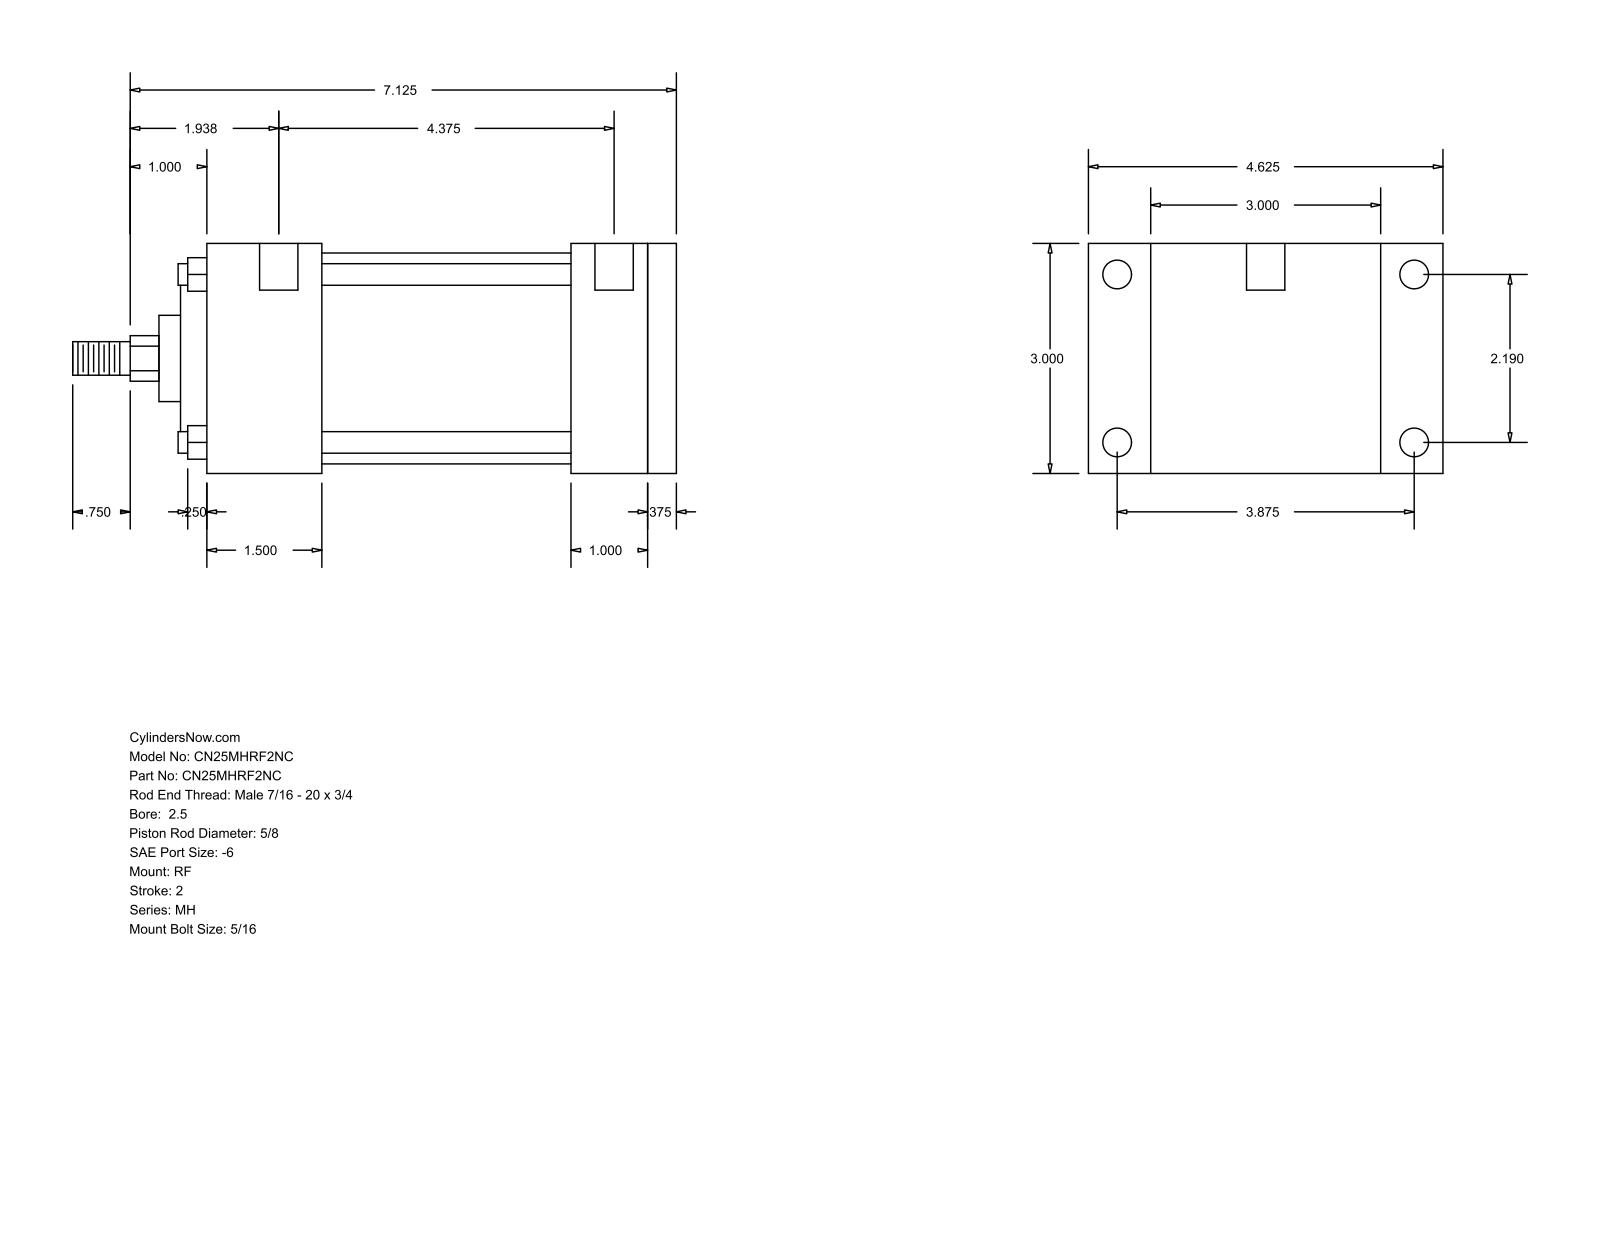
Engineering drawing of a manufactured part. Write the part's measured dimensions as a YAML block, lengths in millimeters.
part_name: "MH_RF__0250_0.625"
step_written_by: "GSSL Pune (CONFIG_CONTROL_DESIGN)"
units: millimeters
bodies: {solids: 0, faces: 94, planar: 65, cylindrical: 29, other: 0}
overall_size: [200.03, 117.47, 76.2]
round_holes:
  - {diameter: 5.56, count: 4}
  - {diameter: 9.53, count: 4}
  - {diameter: 12.7, count: 2}
round_bosses_or_shafts:
  - {diameter: 7.14, count: 4}
  - {diameter: 69.85, count: 1}
  - {diameter: 55.55, count: 1}
  - {diameter: 28.57, count: 1}
  - {diameter: 15.88, count: 1}
  - {diameter: 11.11, count: 1}
partial_cylinders:
  - {radius: 7.54, count: 1}
face_to_face_distances: [76.2, 9.52, 155.57, 146.05, 25.4, 38.1, 82.55, 120.65, 34.92, 107.95]
hole_center_spacings: [55.62, 98.42, 113.05, 119.06, 3.17, 4.76, 111.13, 114.3]
